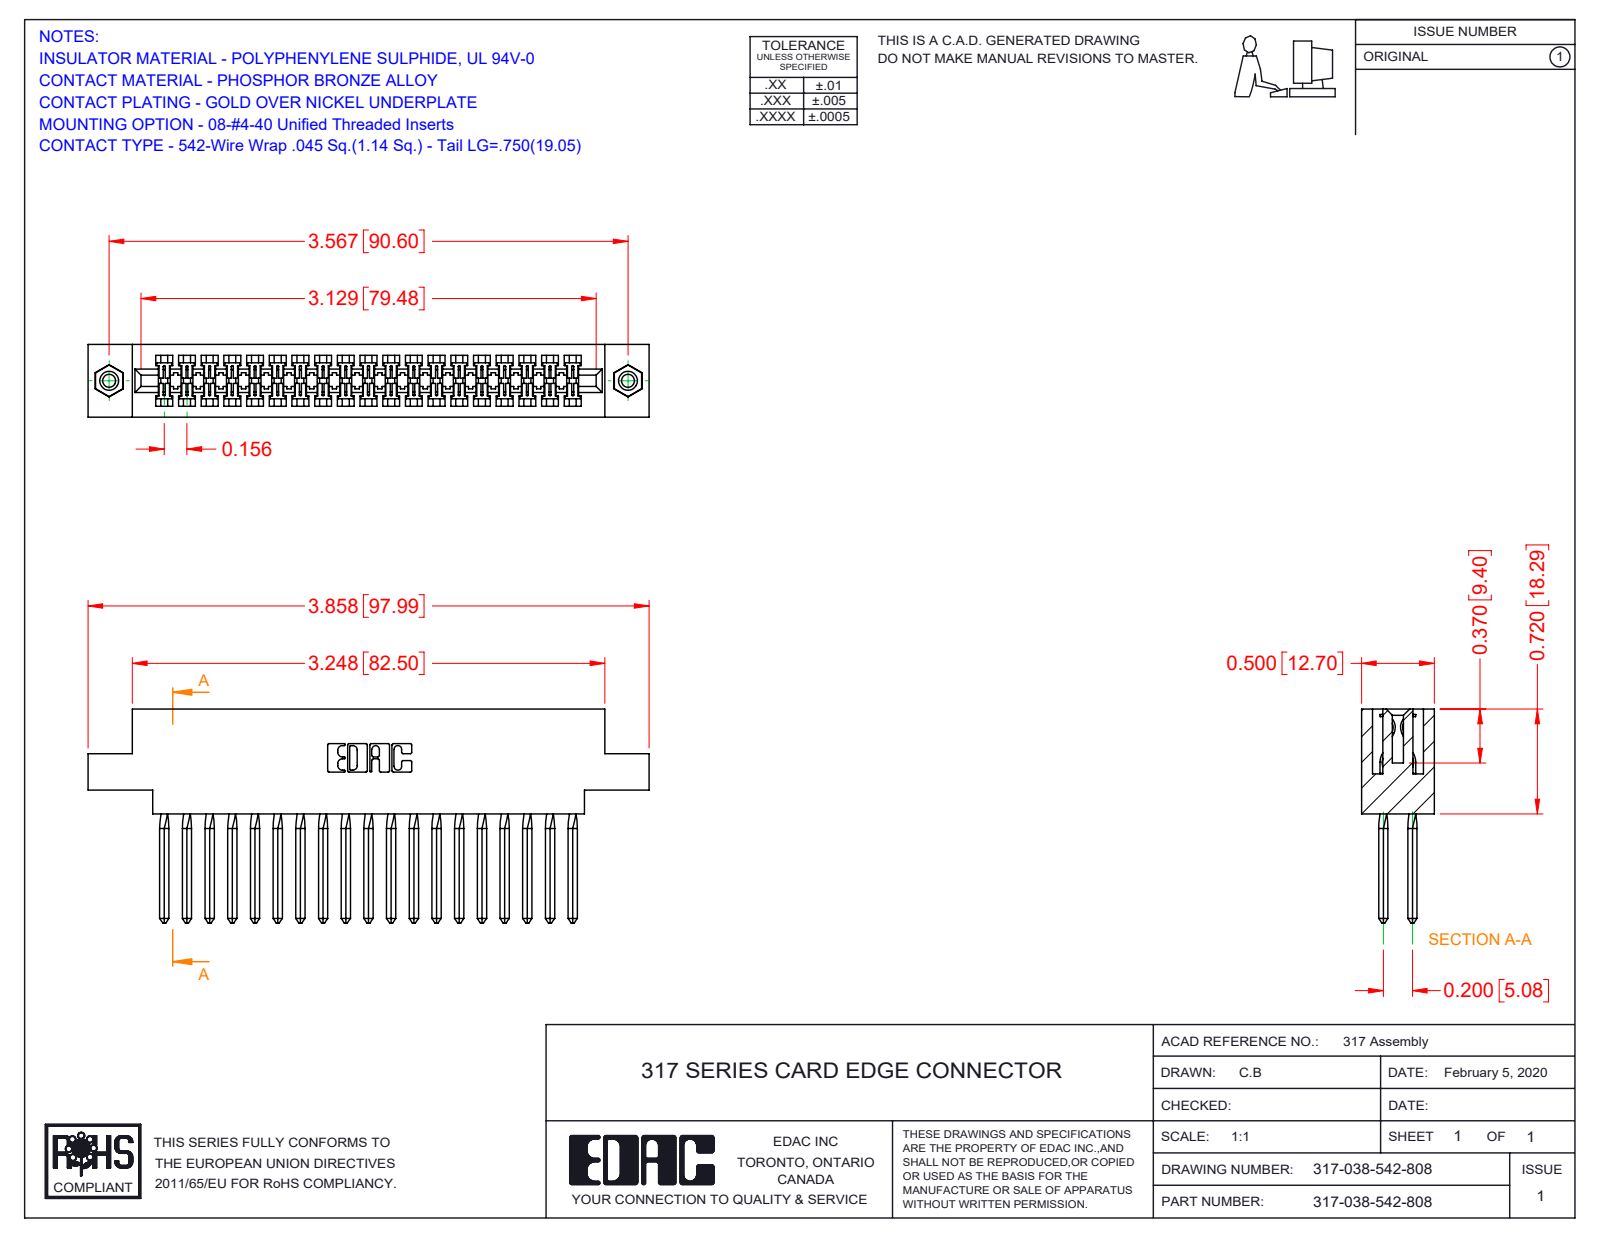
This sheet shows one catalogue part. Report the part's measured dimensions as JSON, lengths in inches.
{"part_name": "345-250-001_345-250-003-102; 317-038-542-808; 317-290-003_542; 317 Part_.156 Dia - TI", "step_written_by": "SolidWorks 2016 (CONFIG_CONTROL_DESIGN)", "units": "inches", "bodies": {"solids": 41, "faces": 2328, "planar": 1838, "cylindrical": 322, "other": 168}, "overall_size": [3.858, 1.47, 0.5], "volume_in3": 0.934, "surface_area_in2": 31.9, "round_holes": [[0.089, 2], [0.125, 2], [0.156, 2]], "round_bosses_or_shafts": [[0.155, 2]], "partial_cylinders_radius": [[0.006, 76], [0.01, 22], [0.007, 6], [0.031, 6], [0.026, 3], [0.074, 2], [0.089, 2], [0.1, 2]], "face_to_face_distances": [0.5, 0.075, 0.425, 0.11, 0.35, 0.2, 0.116, 0.136, 0.72, 0.046], "hole_center_spacings": [3.567]}
